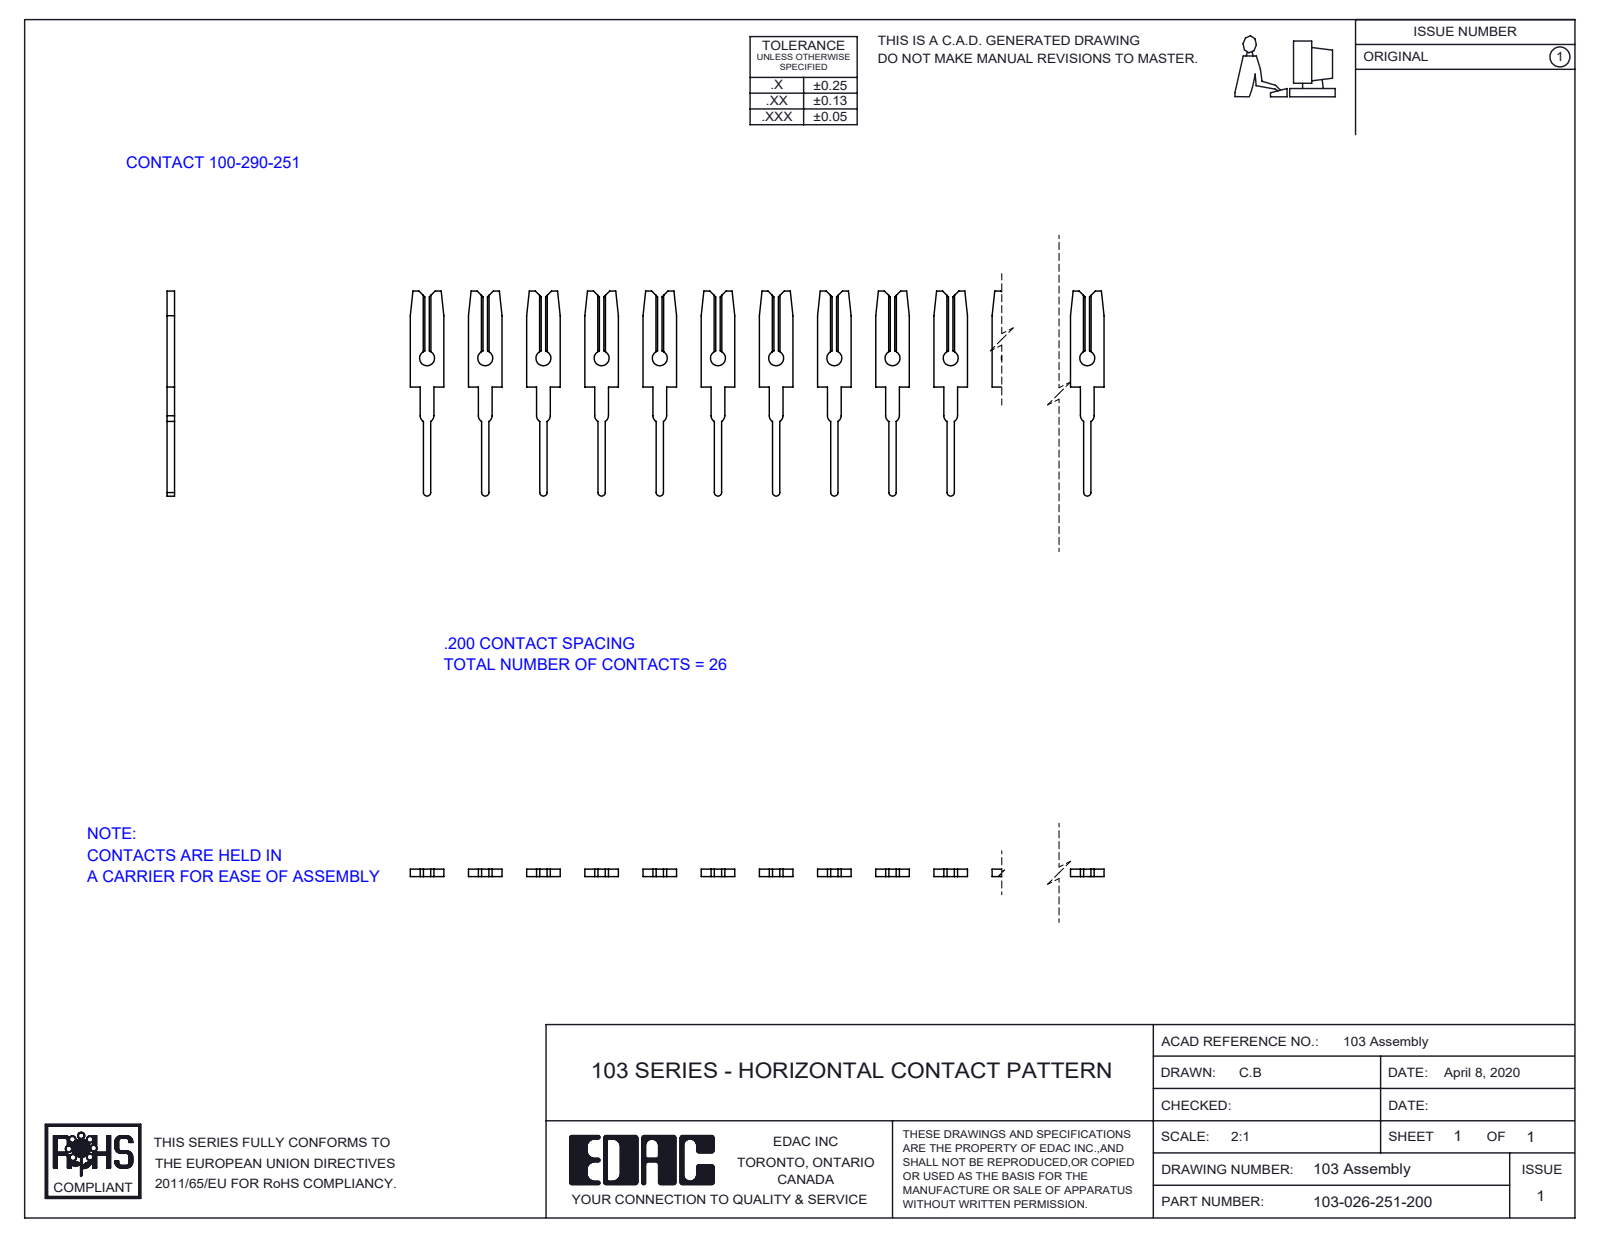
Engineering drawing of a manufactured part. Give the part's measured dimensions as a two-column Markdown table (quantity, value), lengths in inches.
| quantity | value |
| --- | --- |
| part name | 100-290-001_100-290-251; 103-026-251-200 |
| STEP written by | SolidWorks 2016 (CONFIG_CONTROL_DESIGN) |
| units | inches |
| bodies | 26 solids, 728 faces (572 planar, 156 cylindrical, 0 other) |
| overall size | 5.115 × 0.705 × 0.026 |
| volume | 0.029 in³ |
| surface area | 3.622 in² |
| round holes (diameter × count) | 0.052 × 26 |
| partial cylindrical surfaces (radius × count) | 0.012 × 26, 0.024 × 26 |
| main face-to-face distances | 0.026, 0.141, 0.2, 0.4, 0.283, 0.848, 0.6, 0.99, 0.707, 0.8 |
| hole center spacings | 0.2, 0.4, 0.6, 0.8, 1, 1.2, 1.4, 1.6 |
